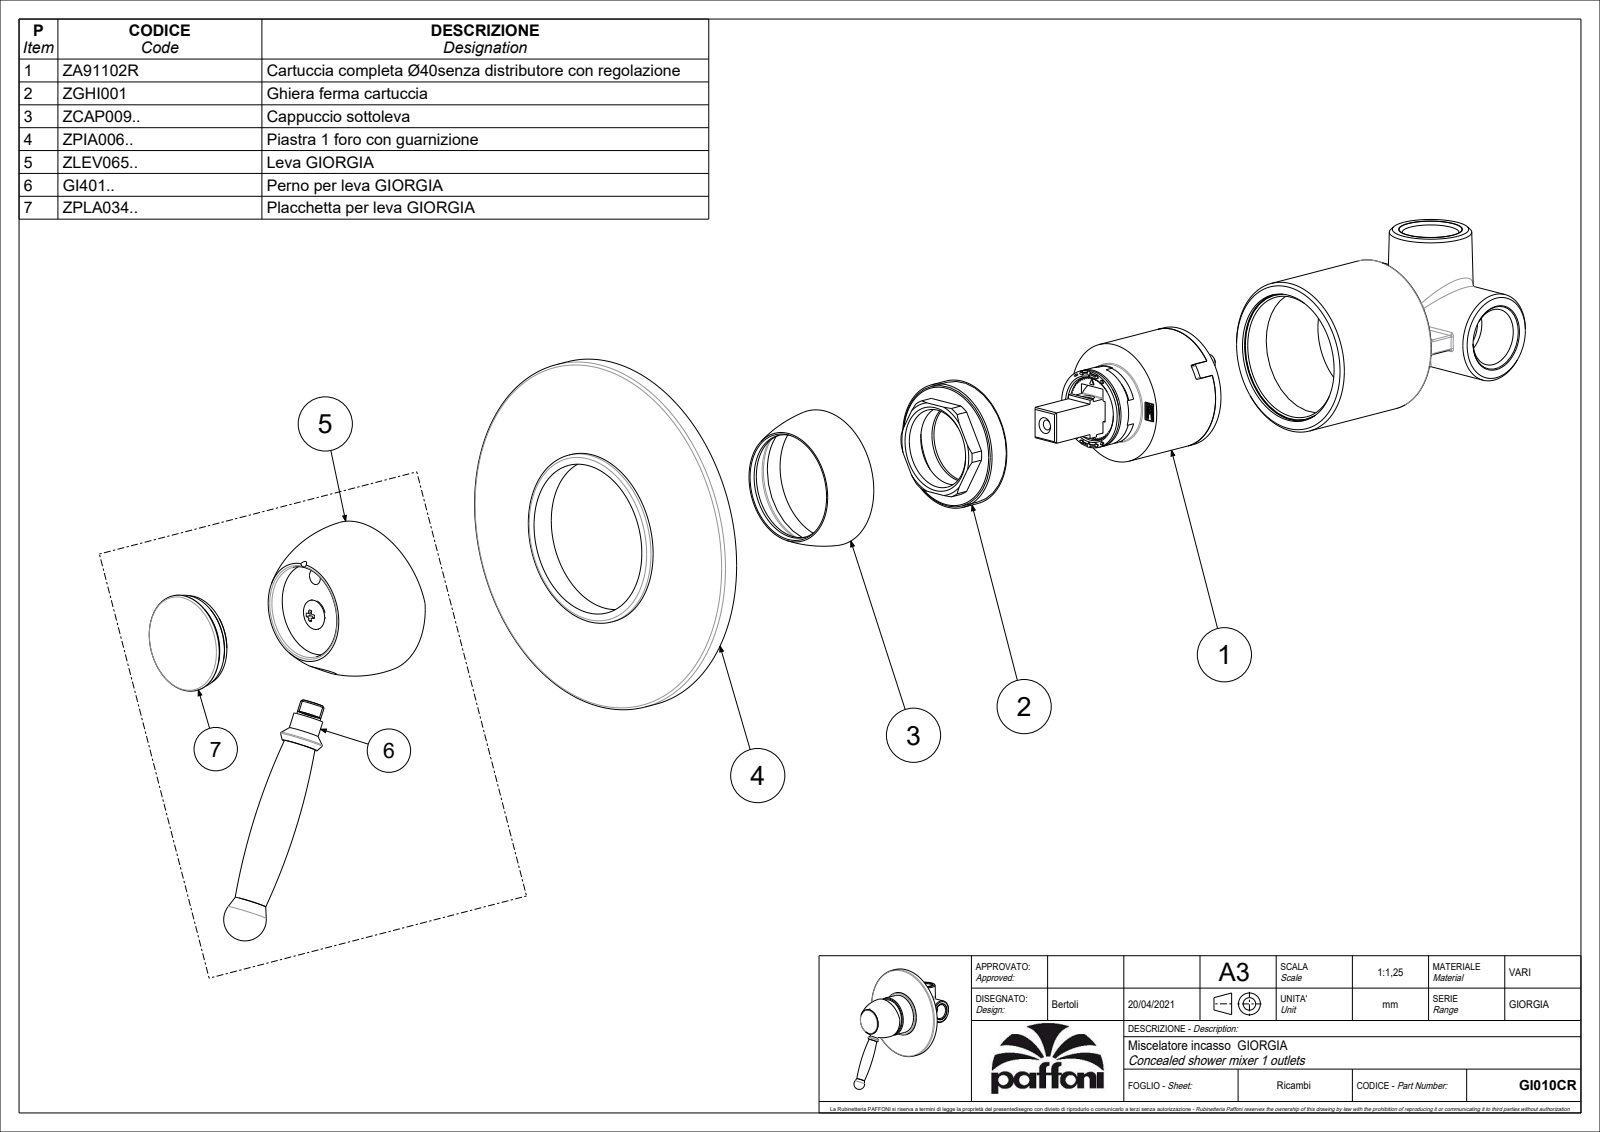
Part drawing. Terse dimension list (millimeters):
name: GI010CR
written by: CREO PARAMETRIC BY PTC INC, 2020044 (CONFIG_CONTROL_DESIGN)
unit: mm
bodies: 1 solid, 966 faces (561 planar, 237 cylindrical, 168 other)
size: 145.9 × 116 × 93.68
volume: 86 977 mm³; area: 72 241 mm²
holes: 3× ⌀5, 2× ⌀8, 1× ⌀3, 1× ⌀3.3, 1× ⌀4, 1× ⌀11, 1× ⌀12, 1× ⌀21, 1× ⌀21.2, 1× ⌀26.1, 1× ⌀30.3, 1× ⌀34.5
bosses: 1× ⌀116, 1× ⌀56.5, 1× ⌀55, 1× ⌀50, 1× ⌀39.5, 1× ⌀36.7, 1× ⌀33, 1× ⌀32
rounds: 26× R0.5, 24× R0.2, 1× R2, 1× R4, 1× R7, 1× R10.05, 1× R11.9, 1× R12.3
face distances: 2.6, 20.9, 8, 21, 55, 24, 21.4, 18.3, 3.1, 34
hole spacings: 8.92, 9.9, 9.99, 14.76, 19.43, 1.47, 1.6, 5.13
